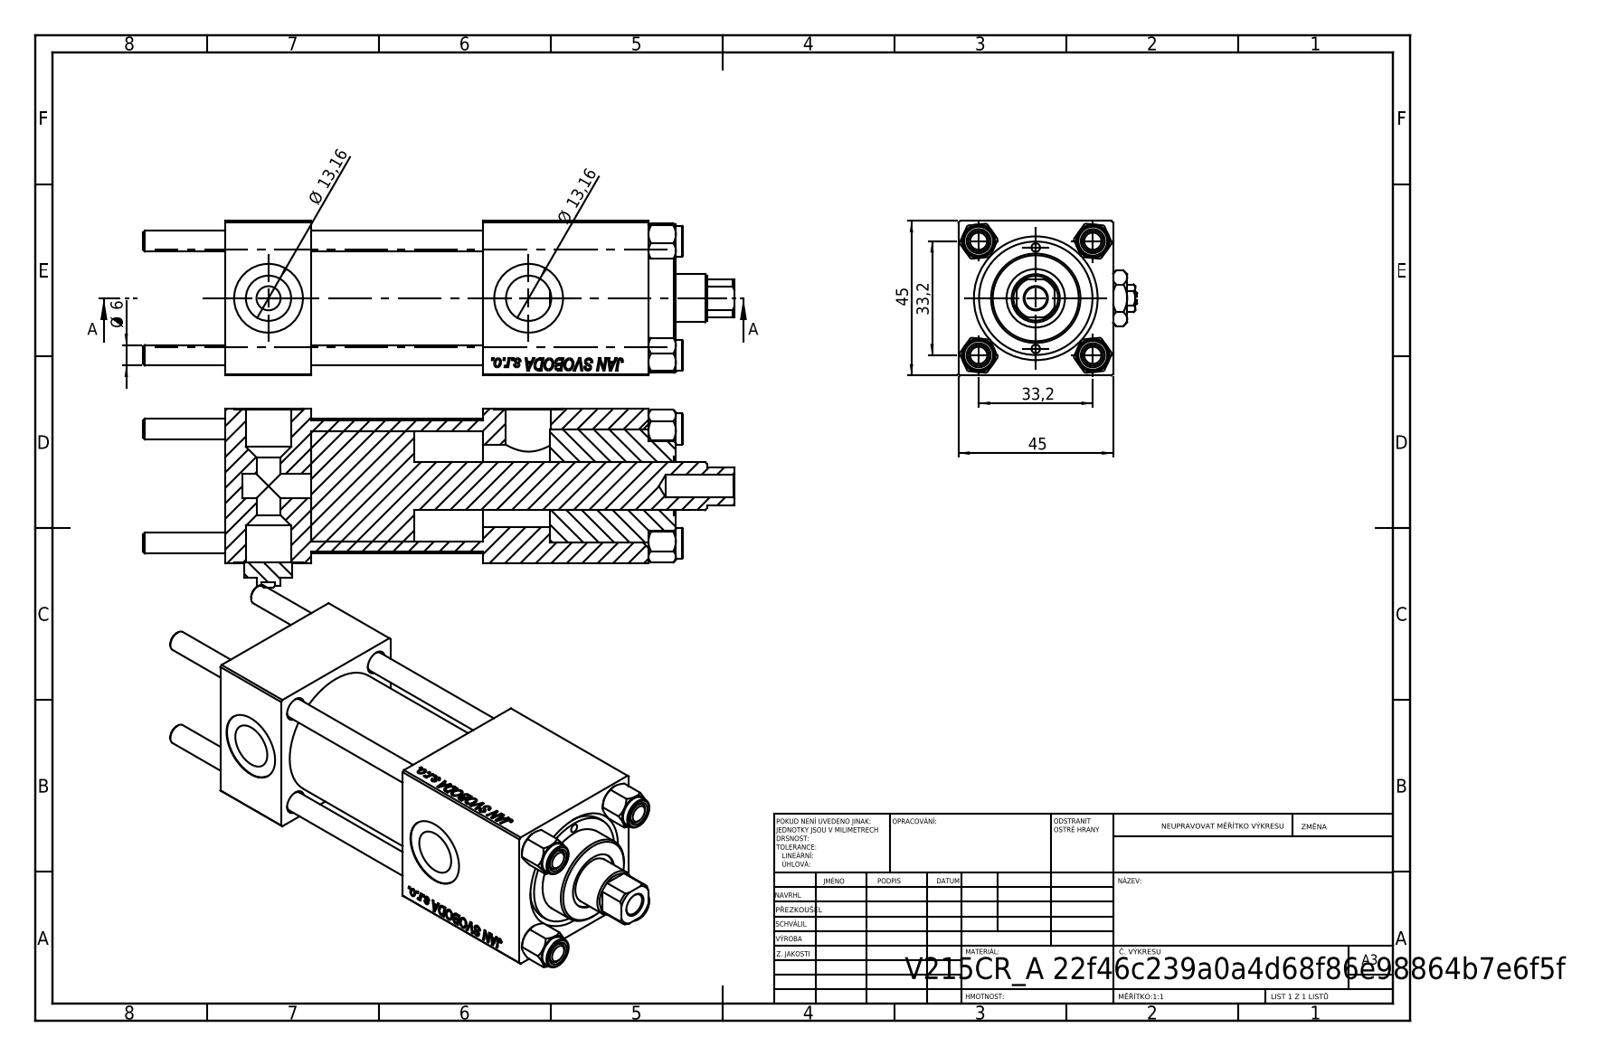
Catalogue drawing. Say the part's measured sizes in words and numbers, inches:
The part is named "Zatka_pro_OIL_PORT; V215CR_BODY_A; V215_VC_A; CR025_012_A_0_G_A_G_M_020_+#_##_TYCINKA (+2 more)". Its 3-D file was written by "SolidWorks 2019 (CONFIG_CONTROL_DESIGN)". It is 12 solids with 1190 faces: 542 planar, 90 cylindrical and 558 other. Overall it measures 6.772 by 2.047 by 1.772 inches. Its volume is 12.02 cubic inches and its surface area 114.7 square inches. Round holes: 4 of diameter 0.236, 2 of diameter 0.098, 2 of diameter 0.276, 2 of diameter 0.518, 2 of diameter 0.787, 1 of diameter 0.256, 1 of diameter 0.512, 1 of diameter 0.551, 1 of diameter 0.669, 1 of diameter 0.945, 1 of diameter 1.26, 1 of diameter 1.299. Round bosses or shafts: 4 of diameter 0.354, 1 of diameter 1.496, 1 of diameter 1.024. Partial cylindrical surfaces (rounded edges, fillets, slot ends): 1 of radius 0.256. The main face-to-face distances are 1.772, 0.984, 4.843, 3.858, 1.969, 2.953, 1.89, 3.713, 2.728, 0.76. The hole center spacings are 0.657, 0.924, 1.307, 1.396, 0.581, 1.848, 1.161, 2.979.
